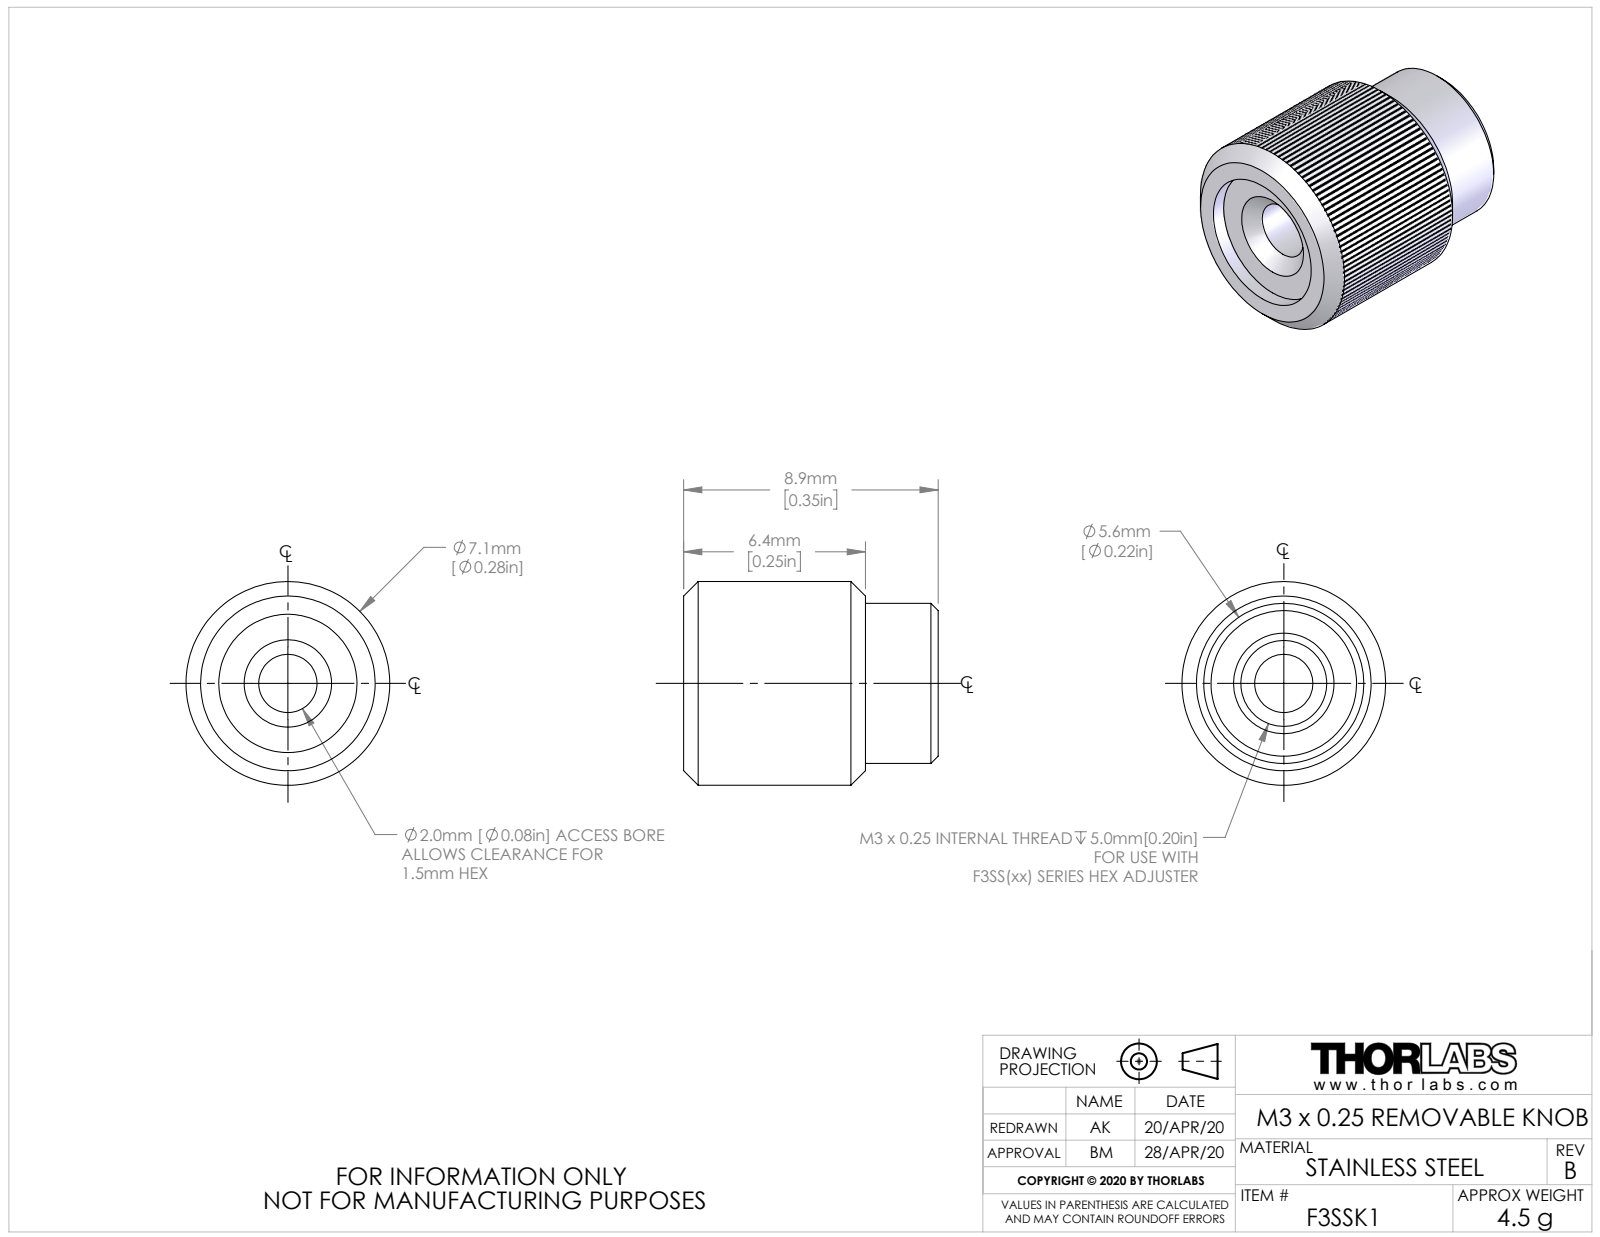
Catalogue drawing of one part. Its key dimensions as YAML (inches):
part_name: "8562-E0W"
step_written_by: "SolidWorks 2018 (AUTOMOTIVE_DESIGN)"
units: inches
bodies: {solids: 1, faces: 28, planar: 6, cylindrical: 12, other: 10}
overall_size: [0.35, 0.28, 0.28]
volume: 0.015
surface_area: 0.497
round_holes:
  - {diameter: 0.08, count: 1}
  - {diameter: 0.118, count: 1}
  - {diameter: 0.132, count: 1}
  - {diameter: 0.19, count: 1}
round_bosses_or_shafts:
  - {diameter: 0.28, count: 1}
  - {diameter: 0.22, count: 1}
face_to_face_distances: [0.02, 0.33, 0.35, 0.1, 0.15, 0.2, 0.13, 0.23, 0.25, 0.18]
